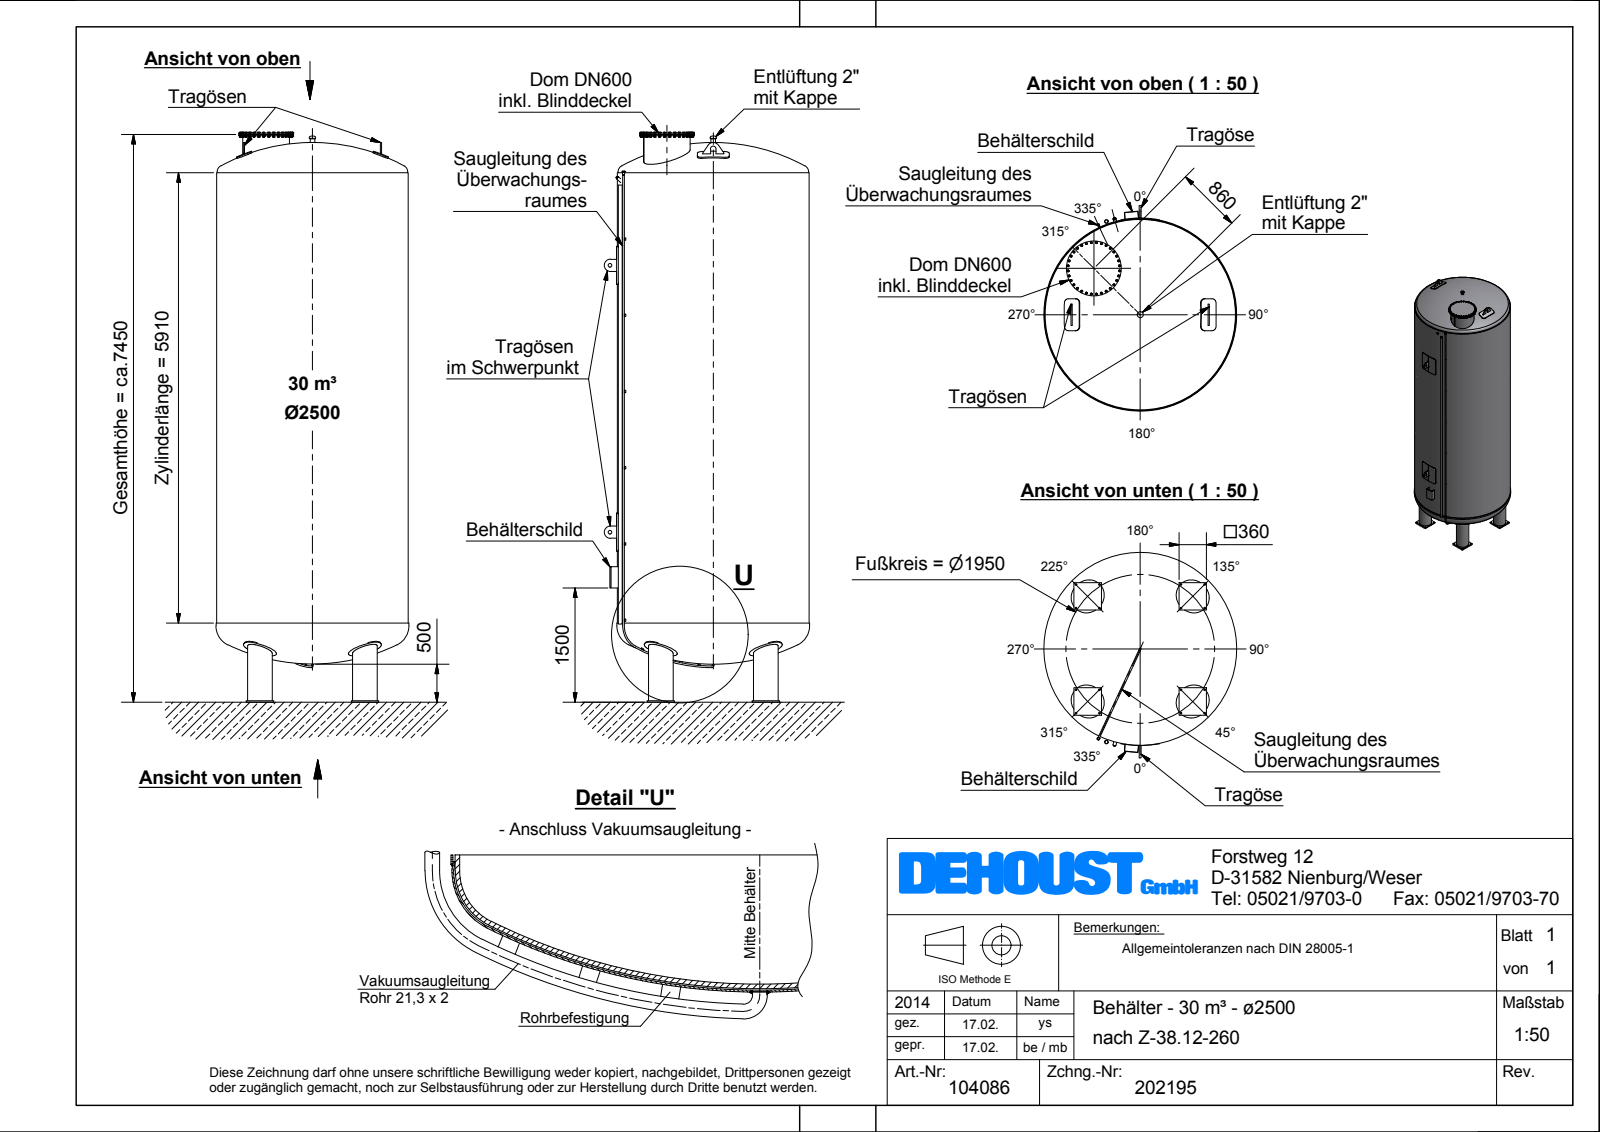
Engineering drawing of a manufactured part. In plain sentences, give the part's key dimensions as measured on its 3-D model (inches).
The part is named "Z-38_12-260_Beh\\S\\dlter_\\S\\x2500_030m\\S\\3_Dichte=1,0". Its 3-D file was written by "Autodesk Inventor 2012 (AUTOMOTIVE_DESIGN)". It is 14 solids with 1225 faces: 723 planar, 164 cylindrical and 338 other. Overall it measures 294.44 by 106.102 by 99.606 inches. Its volume is 1 912 000 cubic inches and its surface area 126 100 square inches. Round holes: 4 of diameter 7.874, 4 of diameter 12.083, 1 of diameter 23.543, 1 of diameter 97.953. Round bosses or shafts: 32 of diameter 0.886, 32 of diameter 0.63, 4 of diameter 17.717, 4 of diameter 12.752, 2 of diameter 0.839, 1 of diameter 99.606, 1 of diameter 99.055, 1 of diameter 98.425. Partial cylindrical surfaces (rounded edges, fillets, slot ends): 8 of radius 1.969, 8 of radius 2.205, 2 of radius 3.15, 1 of radius 1.378, 1 of radius 3.346, 1 of radius 49.567, 1 of radius 49.961. The main face-to-face distances are 273.585, 0.787, 272.798, 294.046, 293.259, 20.461, 291.881, 292.669, 19.083, 1.378. The hole center spacings are 38.386, 54.286, 51.185, 76.772, 4.528, 33.858, 72.244.
